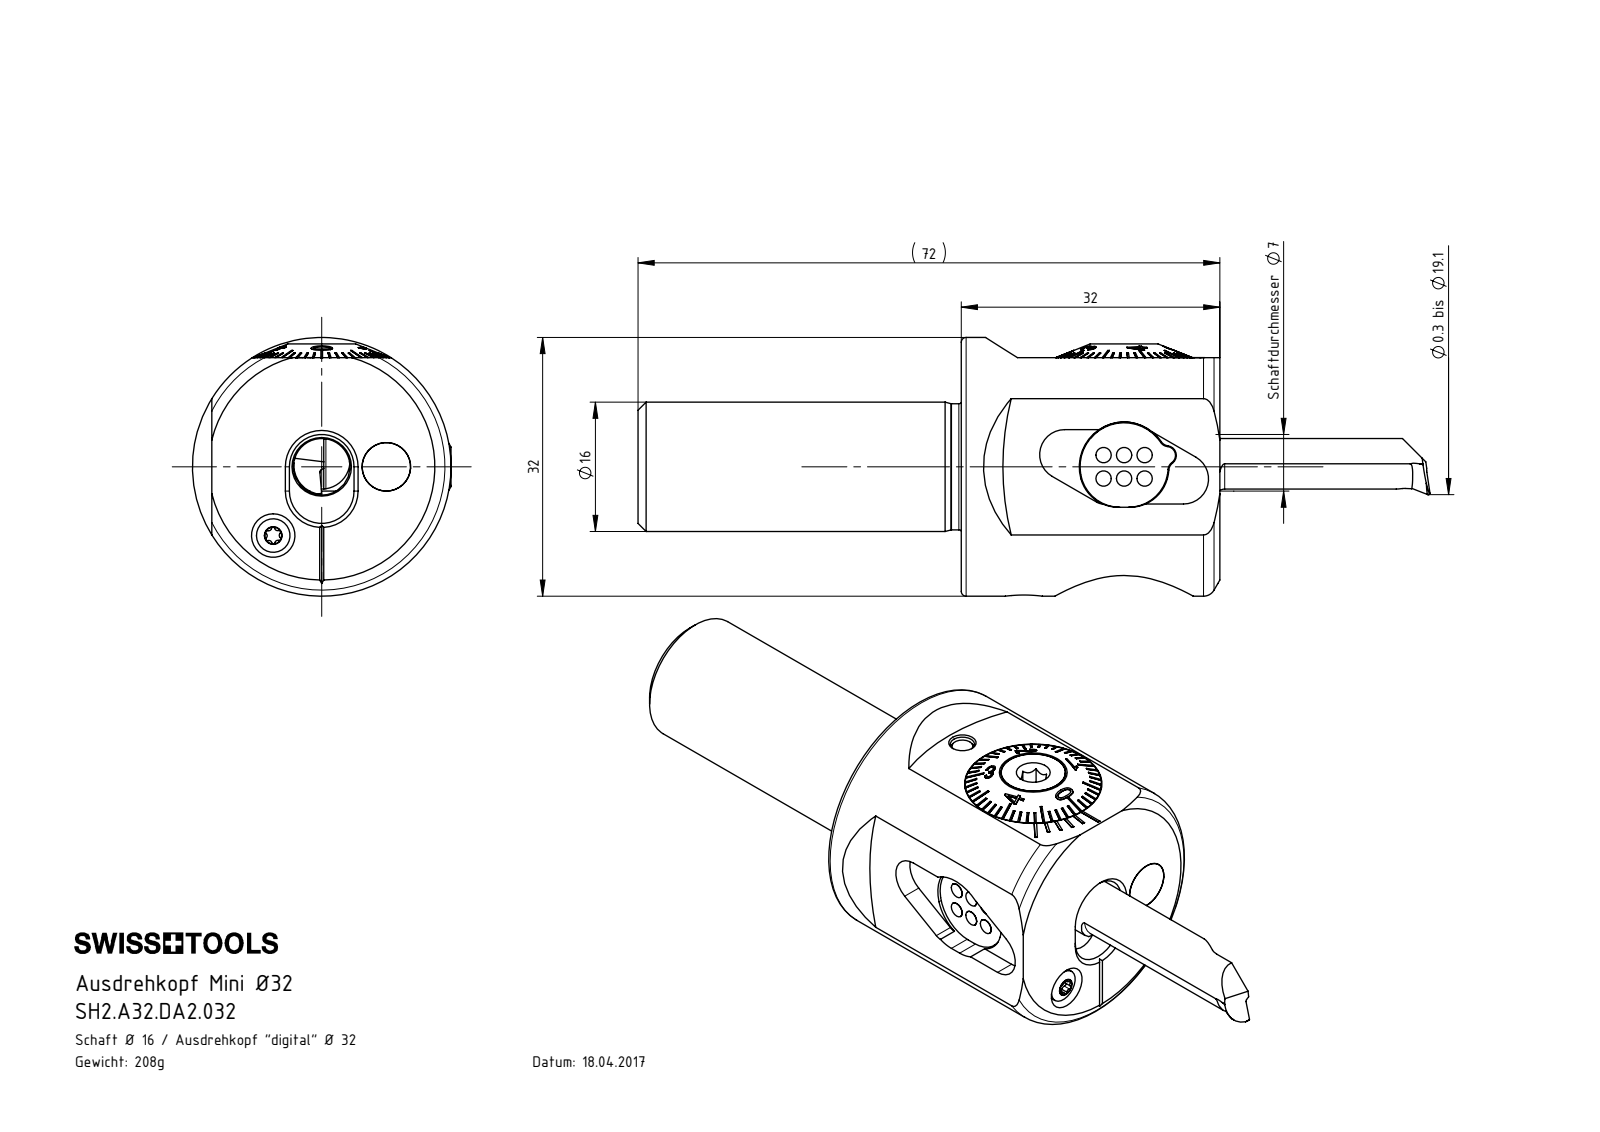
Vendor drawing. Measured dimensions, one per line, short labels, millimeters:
name: A32-BG1.DA1.017_B; Fxx-MAB.xxx.xxx_A_F32x1.3; F32-BG2.017.003_A; WCA-ER2.001.007_A (+8 more)
written by: SolidWorks 2017 (AUTOMOTIVE_DESIGN)
unit: mm
bodies: 17 solids, 804 faces (352 planar, 175 cylindrical, 277 other)
size: 72 × 32 × 32
volume: 27 044 mm³; area: 16 834 mm²
holes: 7× ⌀5, 2× ⌀3.3, 1× ⌀0.7, 1× ⌀1, 1× ⌀2, 1× ⌀2.5, 1× ⌀2.9, 1× ⌀3, 1× ⌀6, 1× ⌀7, 1× ⌀7.75, 1× ⌀8.4
bosses: 6× ⌀1.9, 3× ⌀6, 1× ⌀32, 1× ⌀17, 1× ⌀16.98, 1× ⌀16.85, 1× ⌀16, 1× ⌀15.6
rounds: 6× R0.21, 5× R0.36, 4× R0.2, 4× R2.2, 3× R1.1, 3× R1.2, 2× R3.1, 2× R4
face distances: 32, 4.5, 6.8, 1.5, 3.7, 0.8, 2.3, 2.2, 3, 2.75
hole spacings: 4.5, 6.96, 13, 0.4, 2.61, 2.84, 7.9, 8
